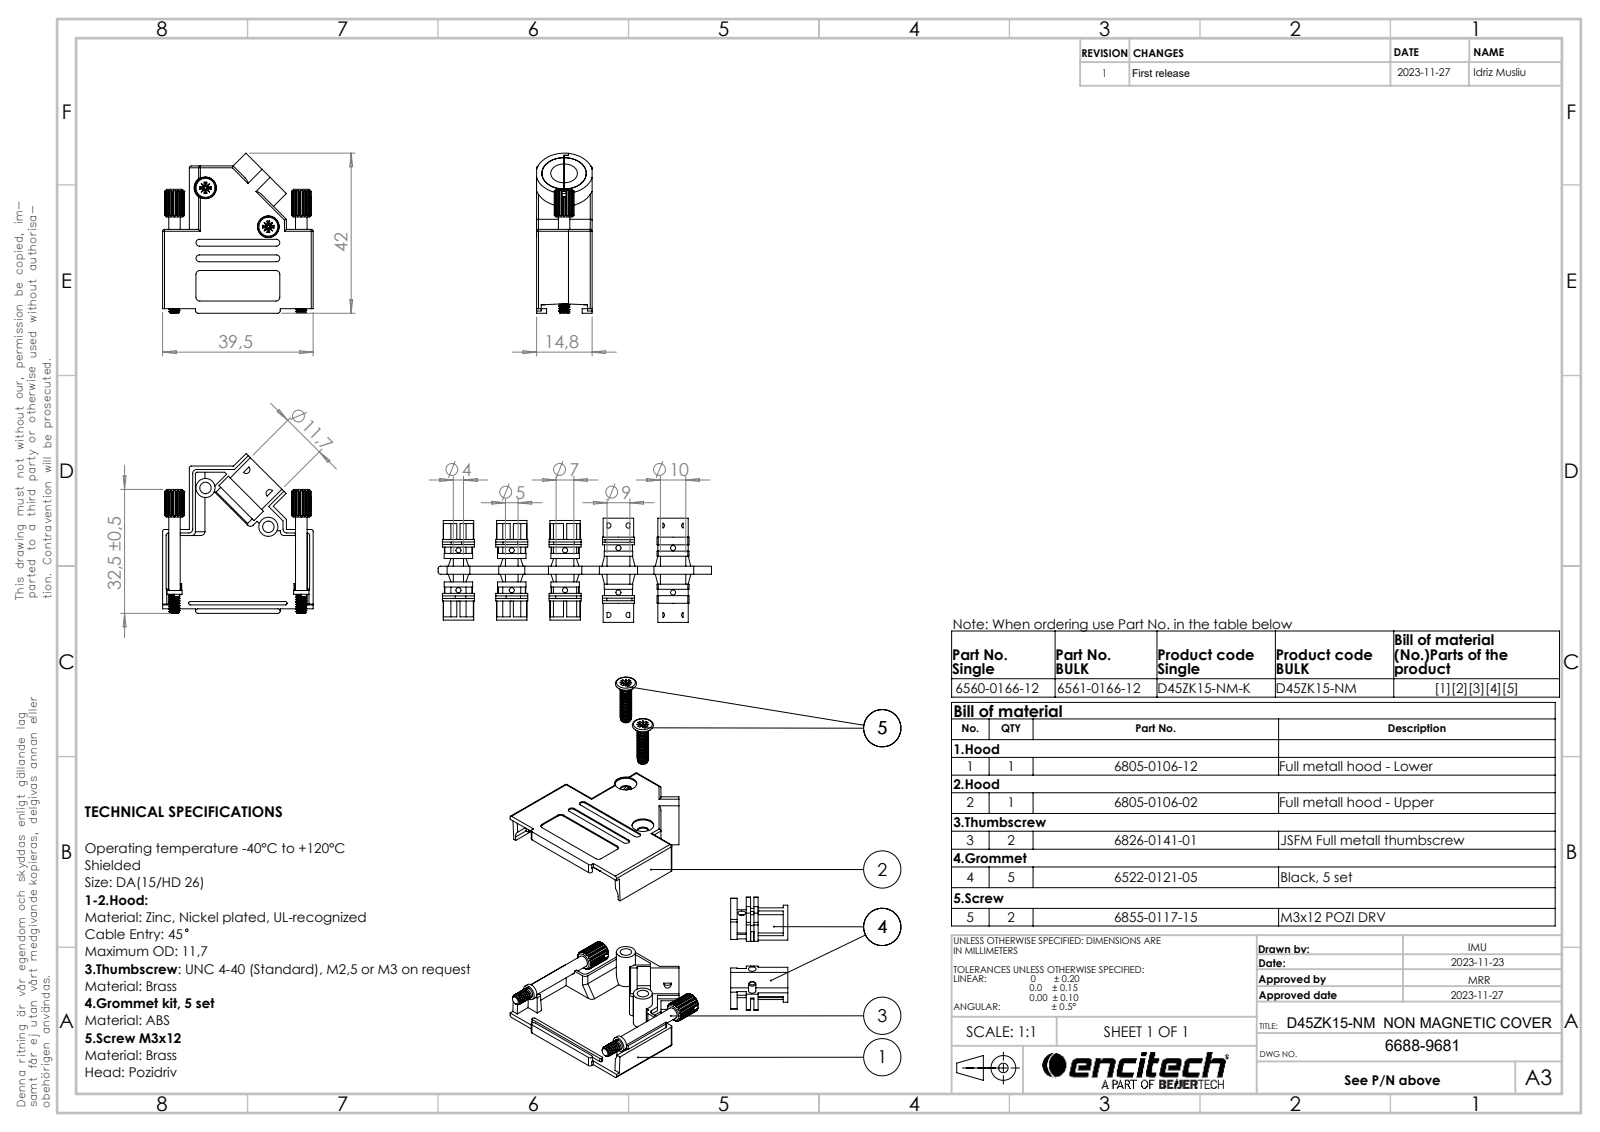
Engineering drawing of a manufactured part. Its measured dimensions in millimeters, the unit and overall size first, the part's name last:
Units: millimetres
Overall size (bounding box): 42 × 39.5 × 14.6
Round holes (diameter × count): ⌀2 ×3, ⌀5.7 ×2, ⌀7 ×1, ⌀11.7 ×1
Round bosses / shafts (diameter × count): ⌀3 ×4, ⌀5 ×2, ⌀4 ×2, ⌀2.8 ×2, ⌀1.9 ×2, ⌀11.6 ×1, ⌀9.2 ×1
Partial cylindrical surfaces — rounded edges, fillets, slot ends (radius × count): R0.5 ×28, R1 ×21, R0.1 ×8, R0.4 ×6, R0.75 ×4, R0.9 ×4, R1.6 ×4, R5.91 ×4
Main face-to-face distances: 1.2, 13.35, 12.15, 14.55, 0.9, 1.6, 14.25, 13.05, 37.9, 7.2
Hole centre spacings: 5.71, 5.31, 5.81, 8.77, 10, 10.64, 14.32, 15.31
Volume: 6 976 mm³ · Surface area: 11 773 mm²
Bodies: 8 solids, 831 faces (454 planar, 298 cylindrical, 79 other)
Part name (STEP PRODUCT): 6805-0106-12; 6805-0106-02; 6826-0141-01; 6522-0121-05 (7mm) (+2 more)
STEP written by: SolidWorks 2021 (AUTOMOTIVE_DESIGN)
